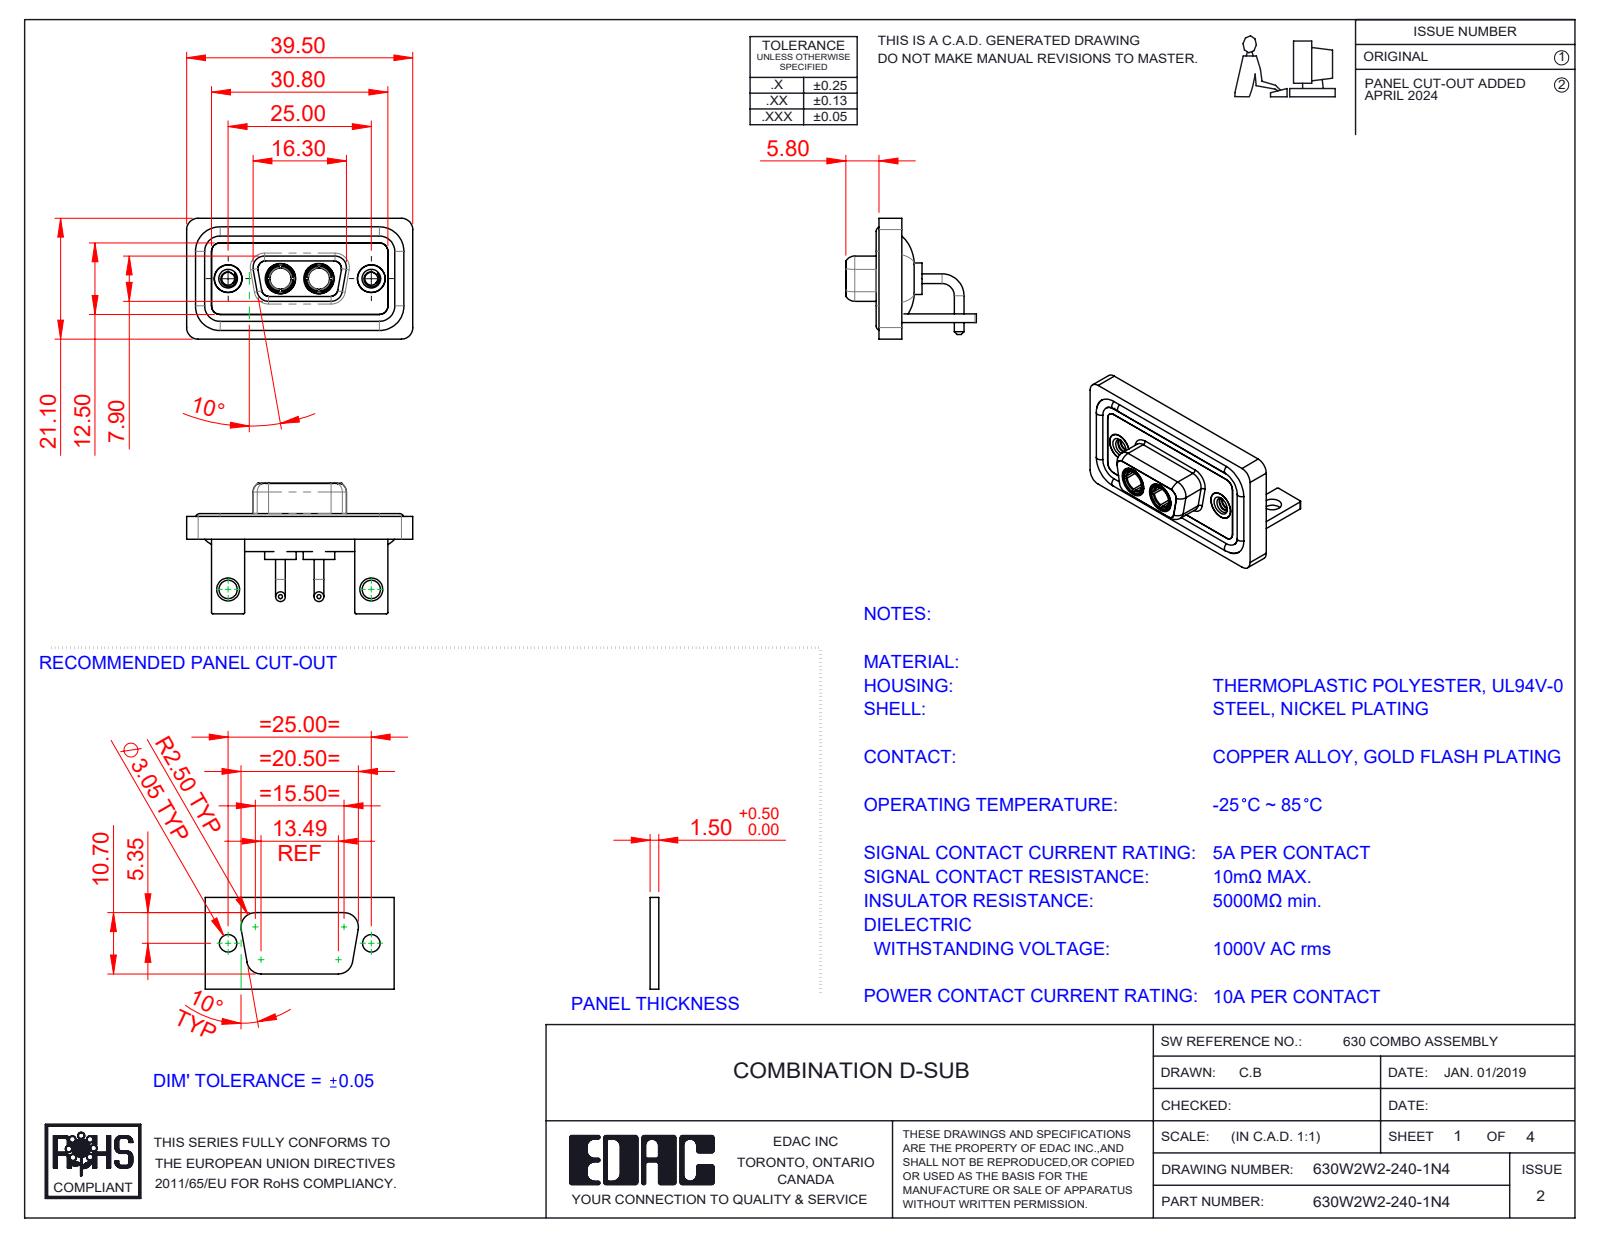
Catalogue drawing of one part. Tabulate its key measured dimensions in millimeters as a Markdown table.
| quantity | value |
| --- | --- |
| part name | 630Combo Shell Front_09 Contacts; 630Combo Waterproof Housing_09 Contacts; 630Combo Threaded Rivet_2; 630W2W2-240-1N4 (+4 more) |
| STEP written by | SolidWorks 2023 (CONFIG_CONTROL_DESIGN) |
| units | millimeters |
| bodies | 13 solids, 590 faces (183 planar, 262 cylindrical, 145 other) |
| overall size | 39.5 × 22.8 × 21.1 |
| volume | 5 067 mm³ |
| surface area | 8 420 mm² |
| round holes (diameter × count) | 4.85 × 4, 2.26 × 2, 3.2 × 2, 3.7 × 2, 4 × 2, 4.05 × 2, 5 × 2, 5.3 × 2 |
| round bosses / shafts (diameter × count) | 1.7 × 4, 1.6 × 4, 5.5 × 2, 5.2 × 2, 4.96 × 2, 4.95 × 2, 4.8 × 2, 4.75 × 2 |
| partial cylindrical surfaces (radius × count) | 2 × 19, 1.5 × 18, 0.25 × 16, 1.35 × 8, 1.6 × 8, 0.5 × 5, 0.6 × 4, 0.65 × 4 |
| main face-to-face distances | 0.4, 2.9, 1.5, 1.8, 1.1, 3.7, 0.8, 2.5, 1.6, 3.1 |
| hole center spacings | 9.14, 15.86, 25, 6.72 |
